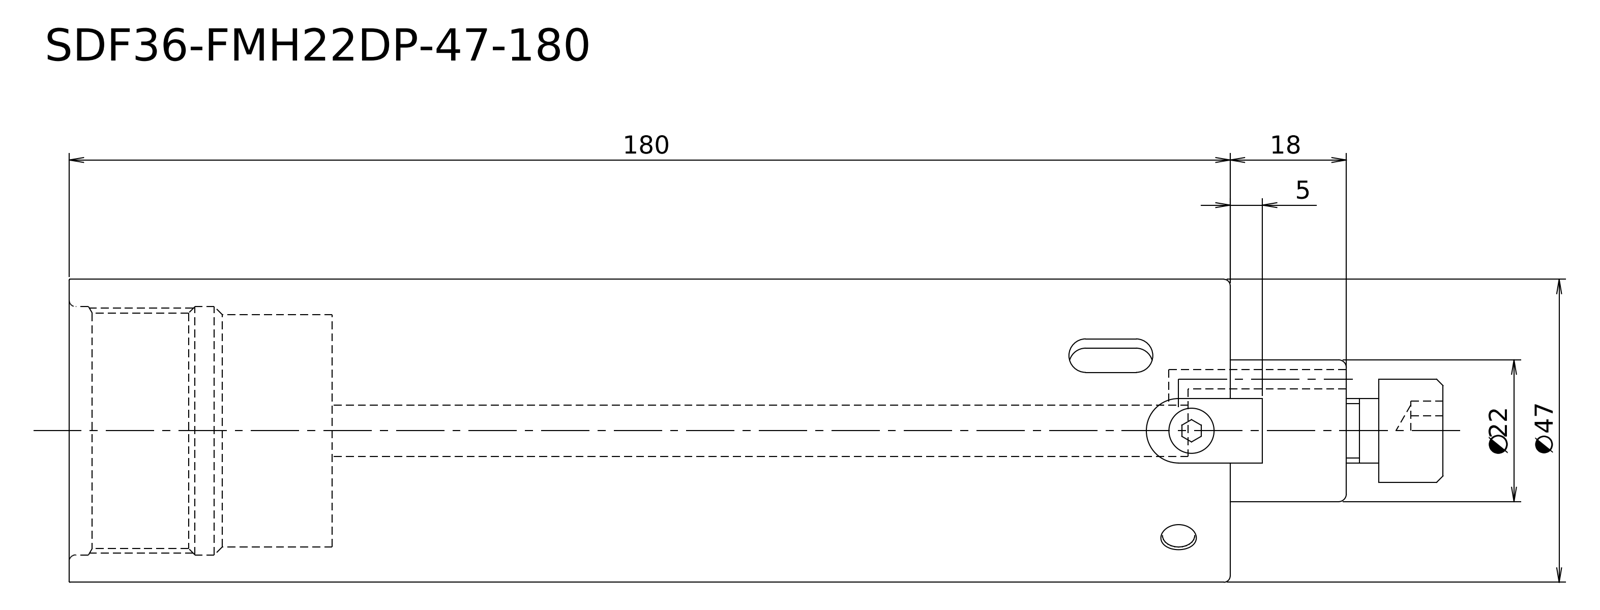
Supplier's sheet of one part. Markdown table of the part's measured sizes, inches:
| quantity | value |
| --- | --- |
| STEP written by | Kubotek KeyCreator V8.5.1 (14335) (CONFIG_CONTROL_DESIGN) |
| units | inches |
| bodies | 1 solid, 5 faces (3 planar, 2 cylindrical, 0 other) |
| overall size | 7.795 × 1.85 × 1.85 |
| volume | 19.47 in³ |
| surface area | 48.5 in² |
| round bosses / shafts (diameter × count) | 1.85 × 1, 0.866 × 1 |
| main face-to-face distances | 7.087, 0.709, 7.795 |
